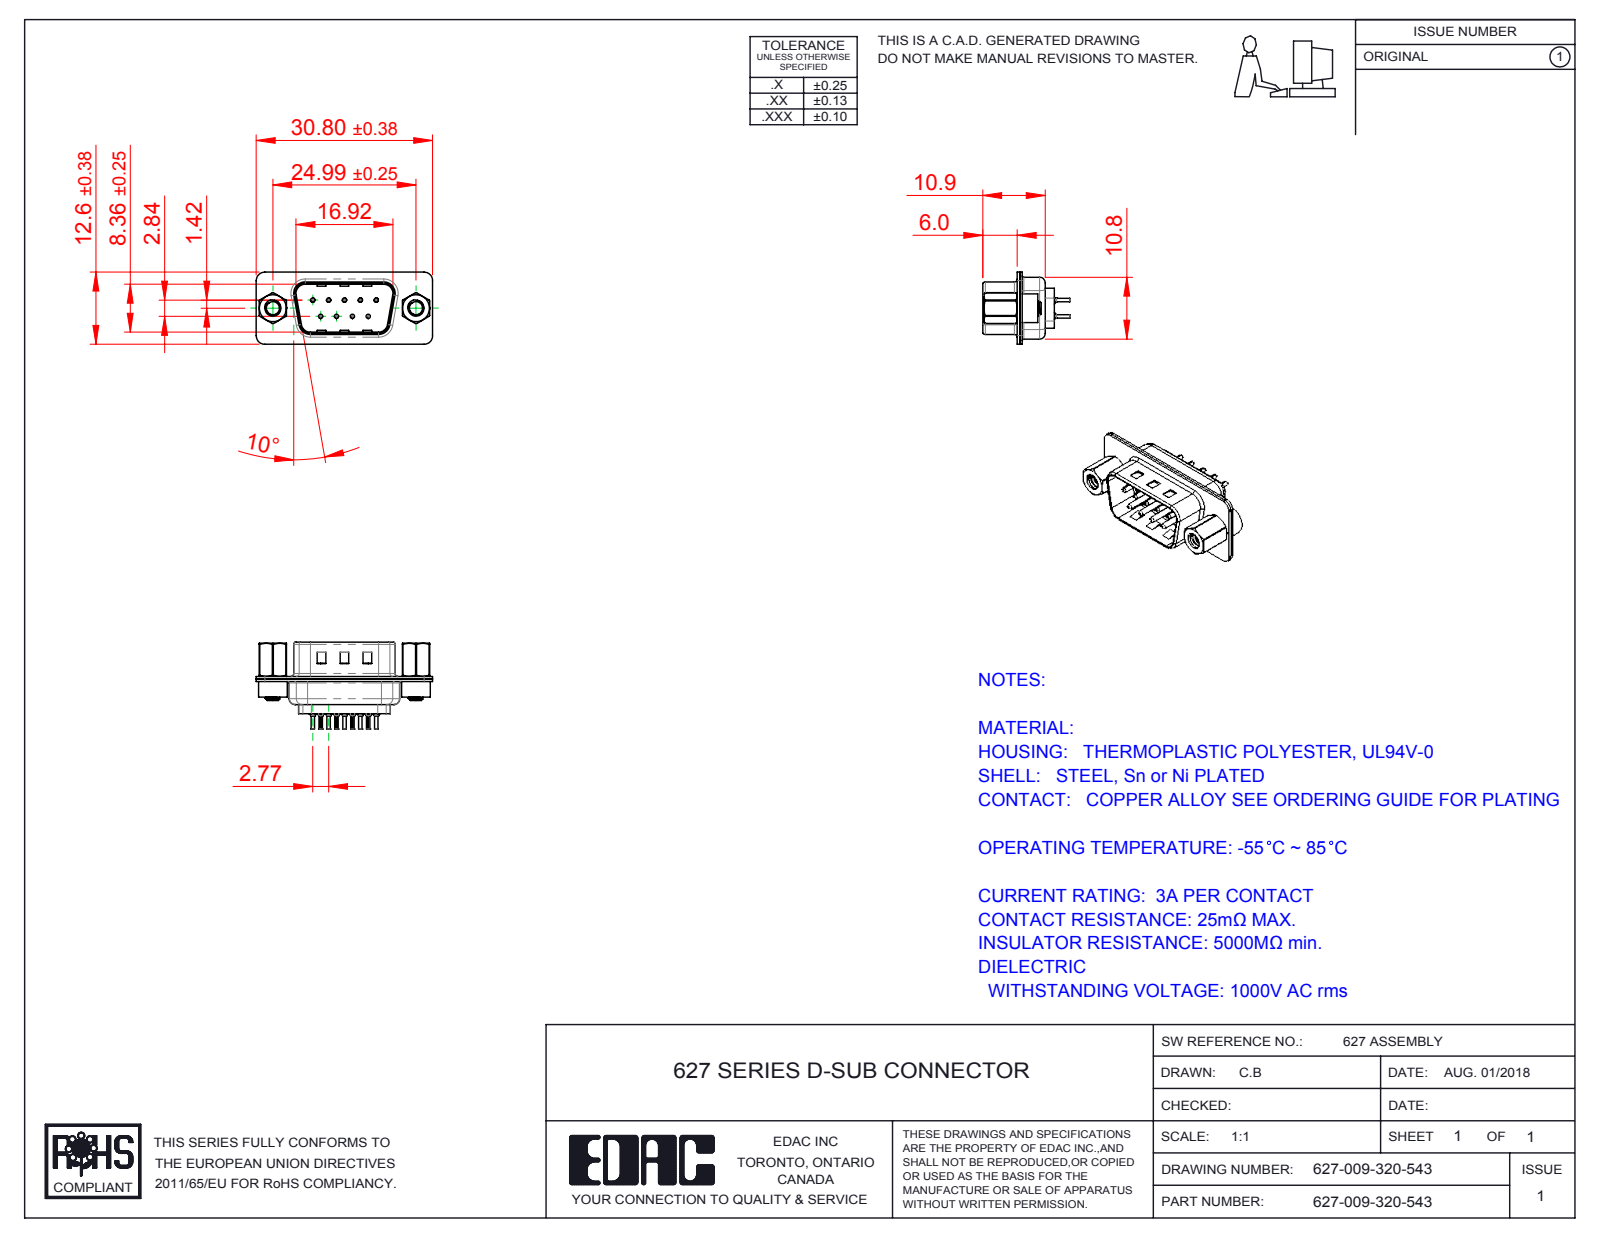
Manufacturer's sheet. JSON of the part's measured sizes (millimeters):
{"part_name": "627 4-40 Threaded Rivet; 627 Shell Rear_09 Contacts; 627 Shell Front_09 Contacts; 627 Contact Row 2_20L (+4 more)", "step_written_by": "SolidWorks 2016 (CONFIG_CONTROL_DESIGN)", "units": "millimeters", "bodies": {"solids": 16, "faces": 1312, "planar": 345, "cylindrical": 534, "other": 433}, "overall_size": [30.8, 15.2, 12.6], "volume_mm3": 1522, "surface_area_mm2": 4369, "round_holes": [[0.2, 9], [0.35, 9], [1.1, 9], [1.6, 9], [2.26, 2], [2.29, 2], [4, 2], [4.8, 2]], "round_bosses_or_shafts": [[2, 9], [1.5, 9], [0.75, 9], [0.6, 9], [5, 2], [4.9, 2], [2.79, 2]], "partial_cylinders_radius": [[0.1, 18], [1.5, 18], [2, 12], [0.5, 8], [1.6, 8], [0.25, 4], [0.6, 4], [0.65, 4]], "face_to_face_distances": [0.45, 0.4, 0.9, 0.82, 9.58, 1.4, 8.76, 0.5, 1.5, 5.6], "hole_center_spacings": [3.16, 2.77, 5.54, 5.03, 5.04, 8.31, 7.48, 7.49]}
